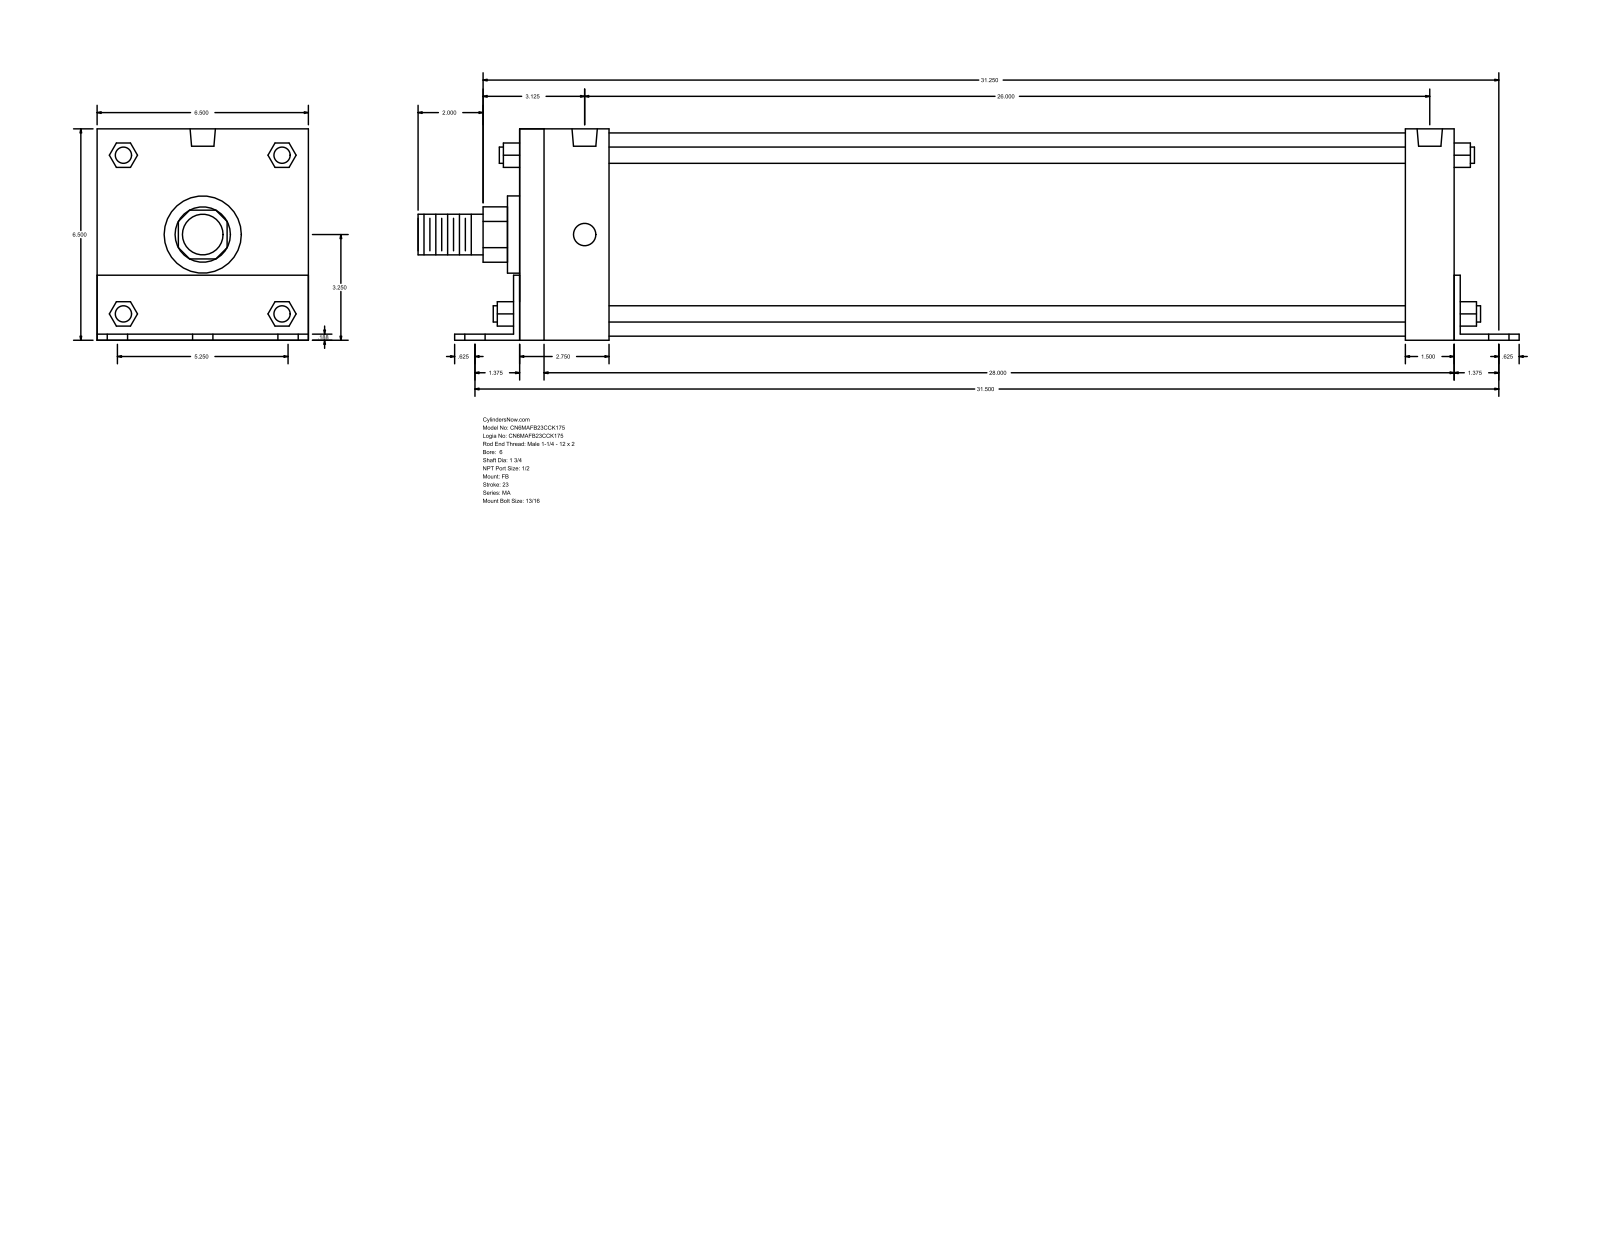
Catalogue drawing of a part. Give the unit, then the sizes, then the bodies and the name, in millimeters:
Units: millimetres
Overall size (bounding box): 860.42 × 165.15 × 165.1
Round holes (diameter × count): ⌀20.64 ×6, ⌀17.46 ×4, ⌀19.77 ×2
Round bosses / shafts (diameter × count): ⌀12.7 ×4, ⌀158.75 ×1, ⌀60.33 ×1, ⌀44.45 ×1, ⌀31.75 ×1
Partial cylindrical surfaces — rounded edges, fillets, slot ends (radius × count): R21.63 ×1, R32.05 ×1
Main face-to-face distances: 165.1, 4.76, 730.26, 165.15, 735.02, 4.71, 160.39, 739.78, 38.1, 69.85
Hole centre spacings: 66.67, 802.87, 800.1, 85.78, 108.6, 133.34, 660.39, 717.47
Bodies: 0 solids, 140 faces (105 planar, 35 cylindrical, 0 other)
Part name (STEP PRODUCT): MA_FB__0600_1.75
STEP written by: GSSL Pune (CONFIG_CONTROL_DESIGN)
